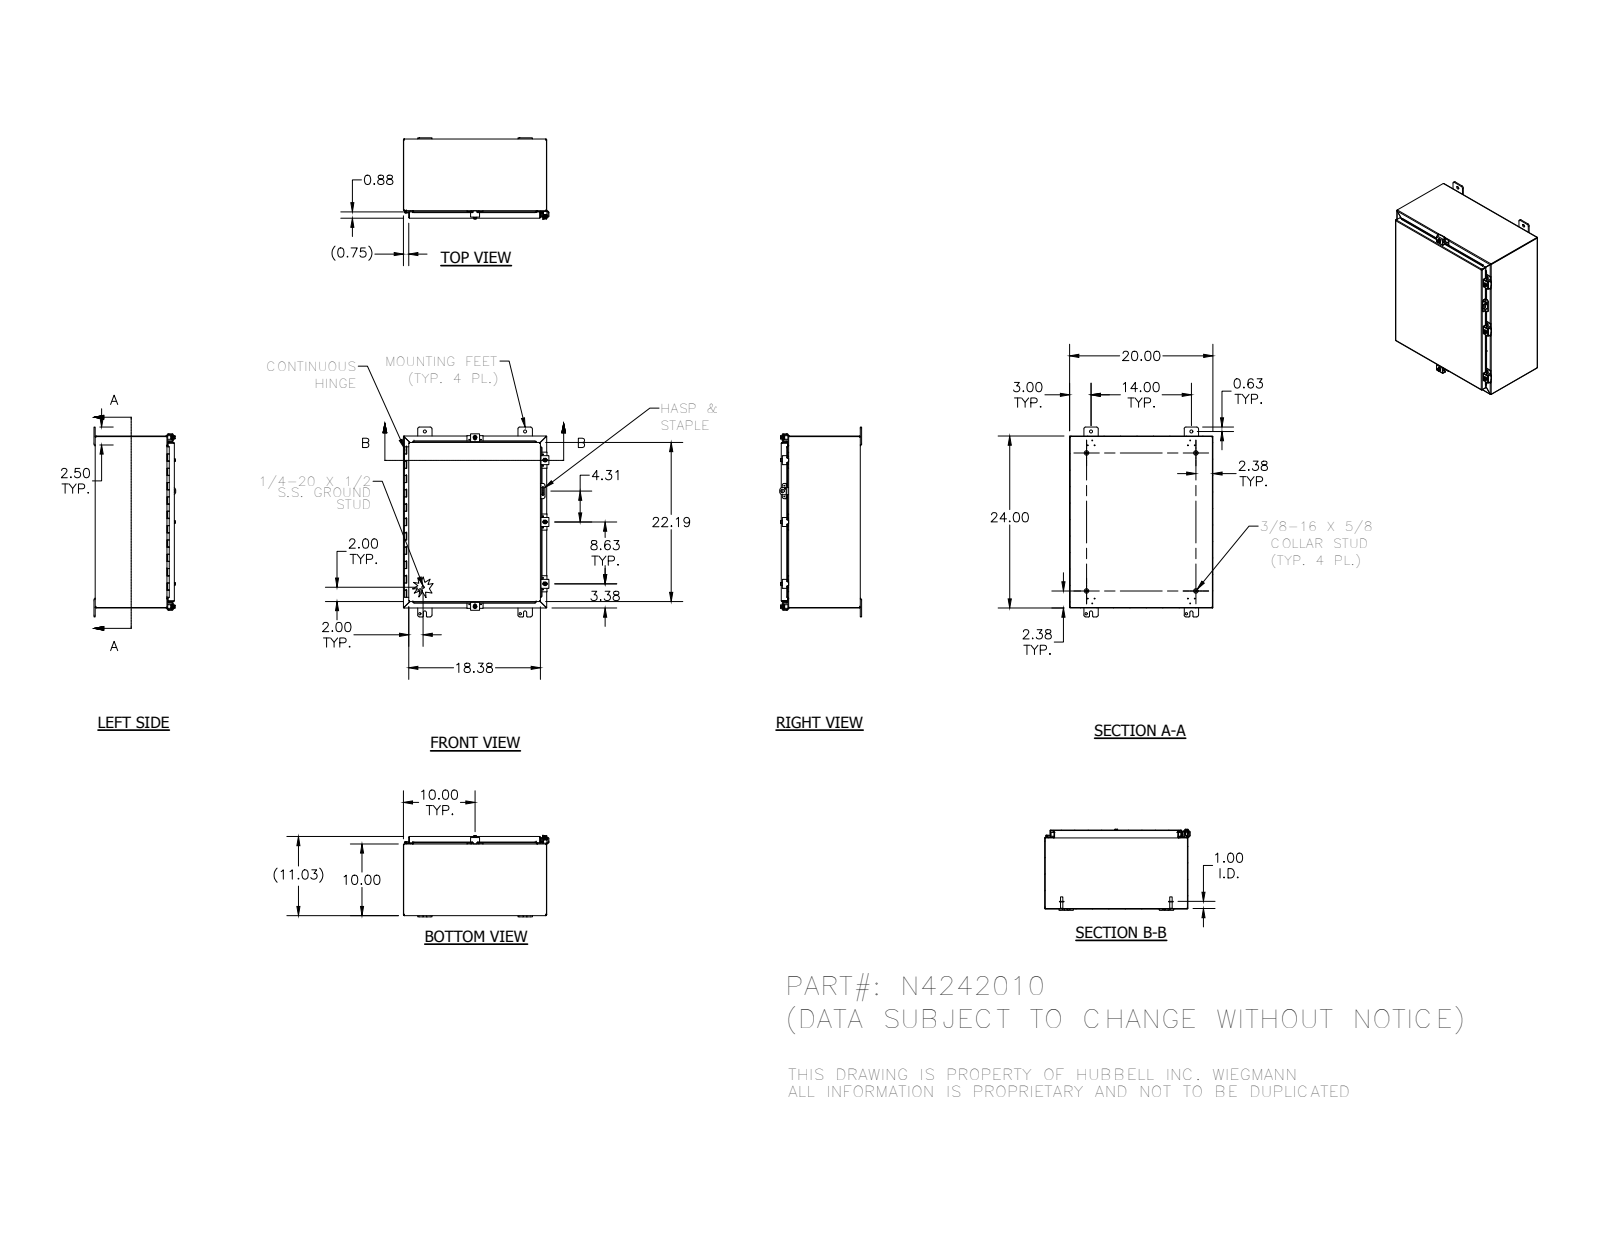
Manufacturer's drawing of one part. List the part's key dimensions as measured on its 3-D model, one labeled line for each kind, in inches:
Part name (STEP PRODUCT): 30817_1; N42420LID_1; 328105T_1; 388116_1 (+8 more)
STEP written by: SolidWorks 2014 (AUTOMOTIVE_DESIGN)
Units: inches
Bodies: 42 solids, 1854 faces (722 planar, 833 cylindrical, 299 other)
Overall size (bounding box): 26.5 × 20.311 × 11.41
Volume: 167.1 in³ · Surface area: 4 370 in²
Round holes (diameter × count): ⌀0.11 ×13, ⌀0.12 ×12, ⌀0.211 ×5, ⌀0.281 ×5, ⌀0.3 ×5, ⌀0.313 ×4, ⌀0.438 ×4, ⌀0.125 ×1, ⌀0.156 ×1, ⌀0.5 ×1
Round bosses / shafts (diameter × count): ⌀0.25 ×7, ⌀0.52 ×5, ⌀0.5 ×5, ⌀0.35 ×5, ⌀0.625 ×4, ⌀0.33 ×4, ⌀0.115 ×2, ⌀0.337 ×1
Partial cylindrical surfaces — rounded edges, fillets, slot ends (radius × count): R0.03 ×61, R0.062 ×37, R0.125 ×35, R0.25 ×31, R0.031 ×23, R0.105 ×23, R0.141 ×10, R0.063 ×8
Main face-to-face distances: 0.074, 10.959, 19.926, 10.885, 11.033, 23.926, 19.852, 20, 9.926, 1.033
Hole centre spacings: 14, 0.876, 0.759, 0.839, 0.94, 0.969, 1.593, 1.995
